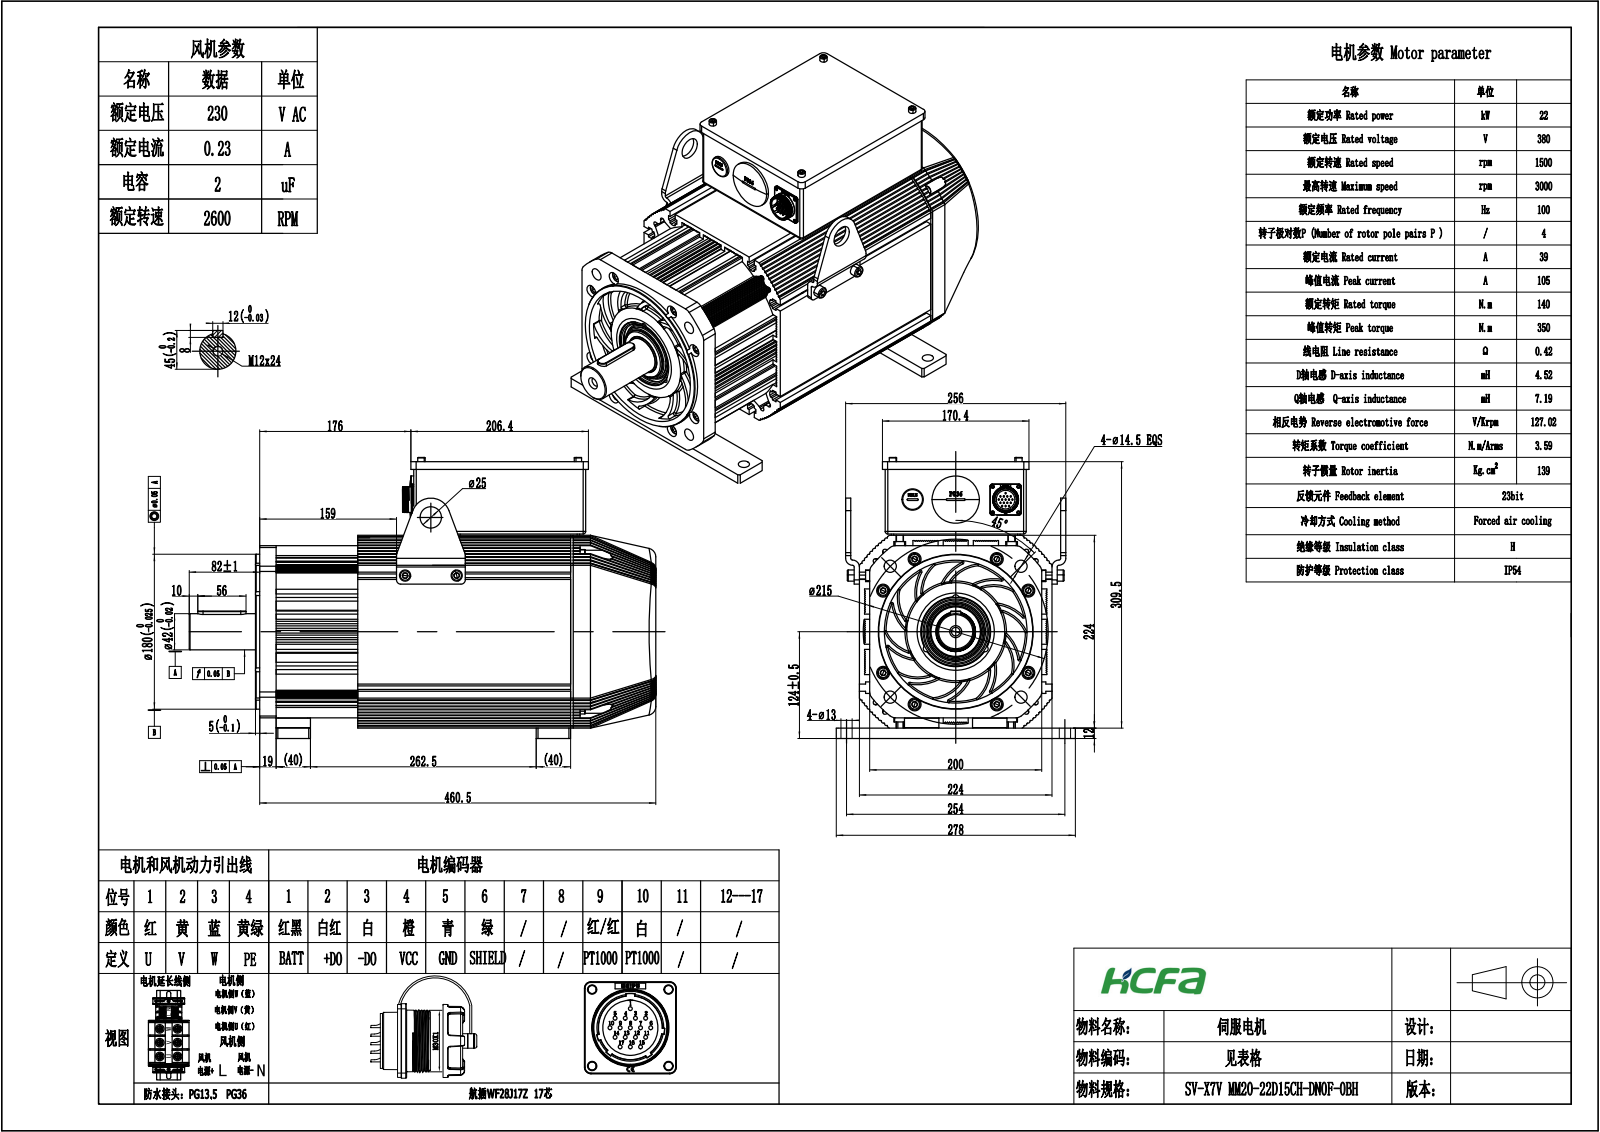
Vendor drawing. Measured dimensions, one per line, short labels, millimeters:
name: 10002030101-0034-SV-X7VMM20-22D15CH-DN0F-0BH-6段外形图
written by: SolidWorks 2021 (CONFIG_CONTROL_DESIGN)
unit: mm
bodies: 8 solids, 3588 faces (1525 planar, 1134 cylindrical, 929 other)
size: 542.5 × 326.5 × 278
volume: 19 440 000 mm³; area: 1 062 000 mm²
holes: 22× ⌀9, 14× ⌀15, 8× ⌀13, 4× ⌀2.5, 4× ⌀5, 4× ⌀6.8, 4× ⌀7, 4× ⌀10, 4× ⌀14.5, 1× ⌀10.2, 1× ⌀20.5, 1× ⌀21.7
bosses: 20× ⌀8, 17× ⌀1.5, 16× ⌀13, 4× ⌀8.5, 3× ⌀10, 3× ⌀6, 2× ⌀40, 1× ⌀180
rounds: 112× R2, 22× R1, 20× R1.5, 18× R5, 16× R1.4, 12× R3, 10× R0.2, 10× R10
face distances: 2, 224, 307.5, 12, 6, 309.5, 212, 30, 194, 32
hole spacings: 29.47, 43.17, 97, 124.07, 137.18, 138.41, 162.9, 167.15
